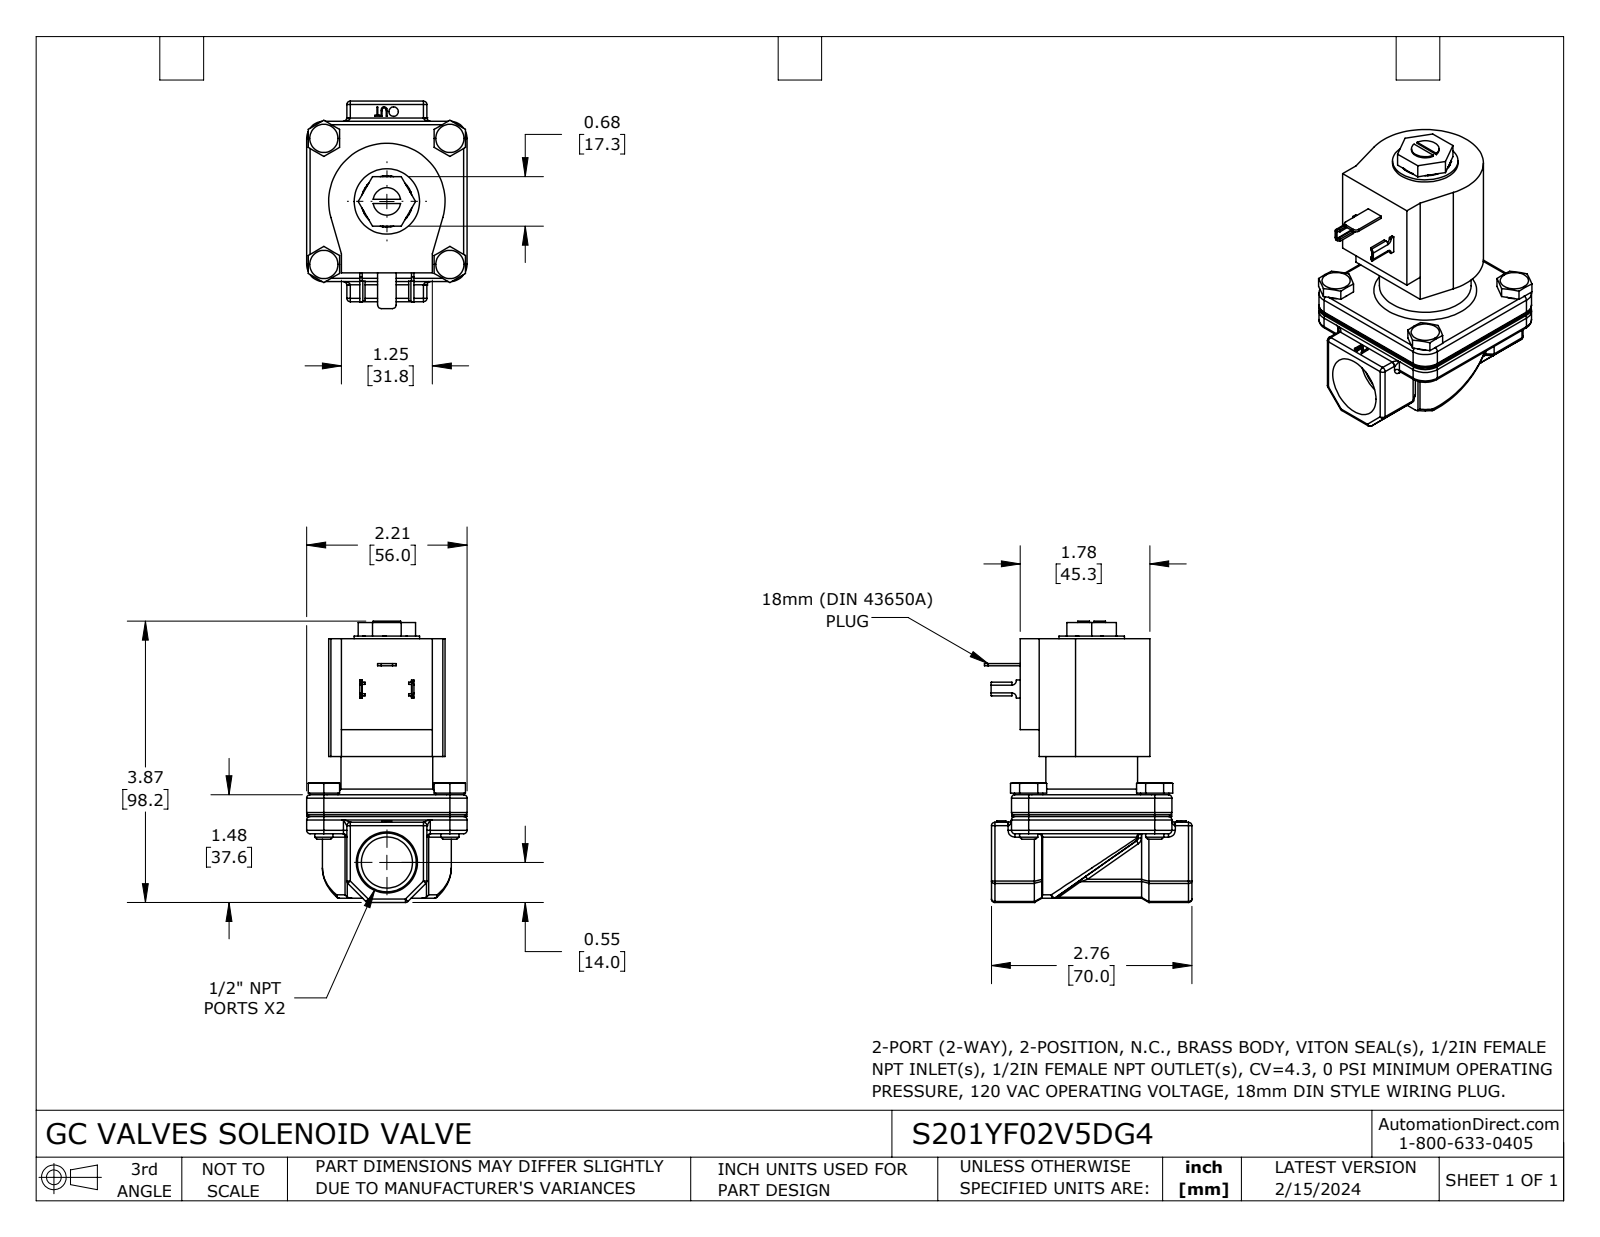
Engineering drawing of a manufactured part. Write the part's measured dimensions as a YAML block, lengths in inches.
part_name: "S201YF02V5DG4"
step_written_by: "SolidWorks 2023 (CONFIG_CONTROL_DESIGN)"
units: inches
bodies: {solids: 1, faces: 507, planar: 201, cylindrical: 158, other: 148}
overall_size: [3.867, 2.851, 2.205]
volume: 9.425
surface_area: 42.81
round_holes:
  - {diameter: 0.703, count: 1}
  - {diameter: 0.706, count: 1}
round_bosses_or_shafts:
  - {diameter: 0.388, count: 4}
  - {diameter: 0.25, count: 4}
  - {diameter: 1.26, count: 1}
  - {diameter: 0.9, count: 1}
  - {diameter: 0.464, count: 1}
  - {diameter: 0.38, count: 1}
partial_cylinders:
  - {radius: 0.047, count: 64}
  - {radius: 0.006, count: 4}
  - {radius: 0.031, count: 4}
  - {radius: 0.041, count: 4}
  - {radius: 0.234, count: 4}
  - {radius: 0.236, count: 4}
  - {radius: 0.05, count: 2}
  - {radius: 0.06, count: 2}
face_to_face_distances: [2.143, 0.059, 0.551, 1.654, 0.537, 2.68, 2.205, 1.06, 0.523, 1.62]
